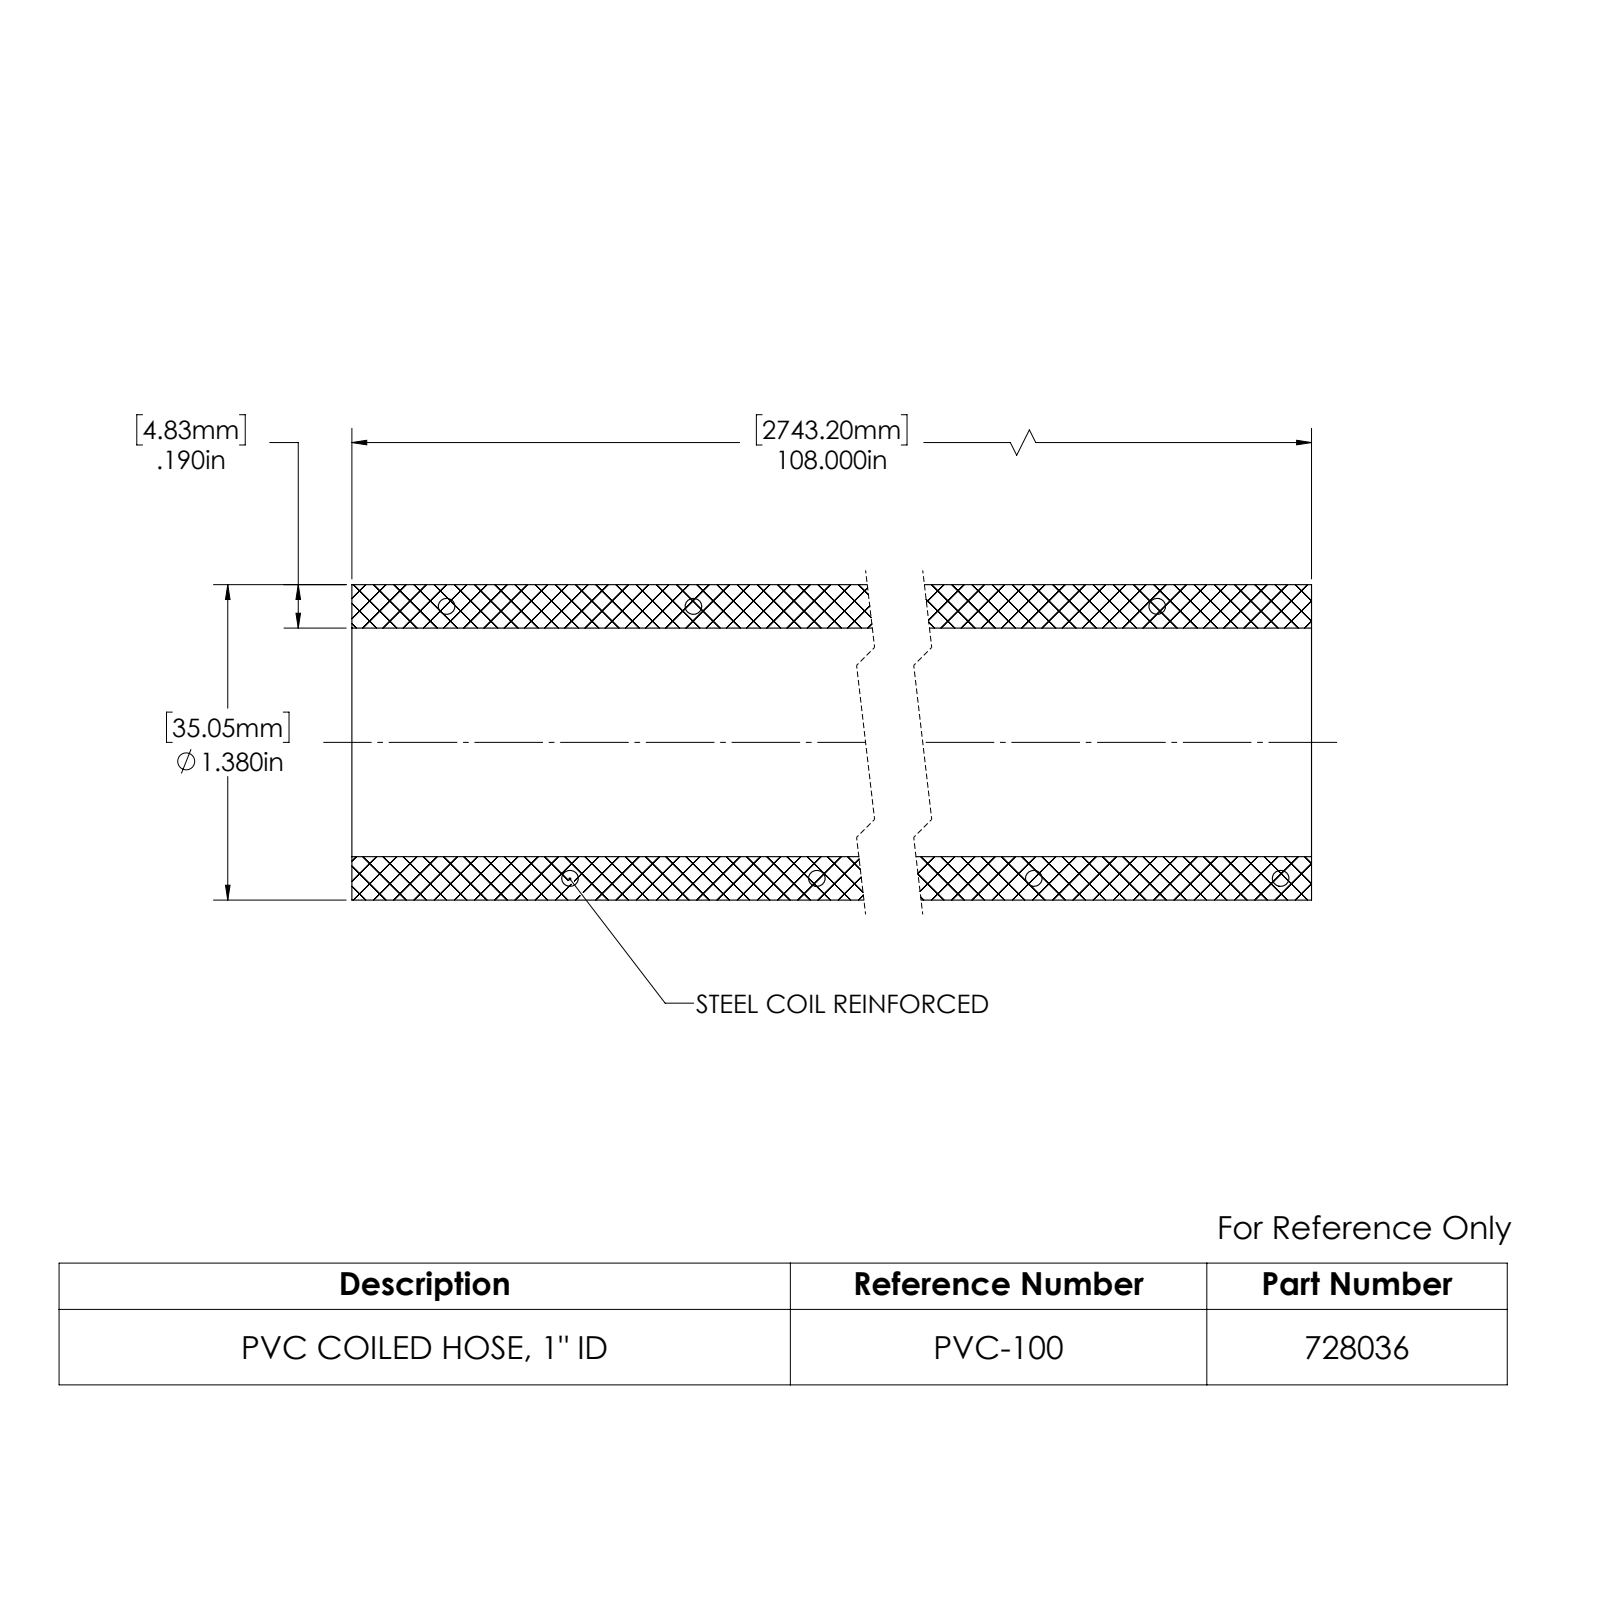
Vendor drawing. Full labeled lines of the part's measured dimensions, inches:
Part name (STEP PRODUCT): 728036
STEP written by: SolidWorks 2022 (CONFIG_CONTROL_DESIGN)
Units: inches
Bodies: 2 solids, 10 faces (4 planar, 4 cylindrical, 2 other)
Overall size (bounding box): 108.024 × 1.38 × 1.38
Volume: 78.21 in³ · Surface area: 894.4 in²
Round holes (diameter × count): ⌀1 ×1
Round bosses / shafts (diameter × count): ⌀1.38 ×1
Main face-to-face distances: 108
